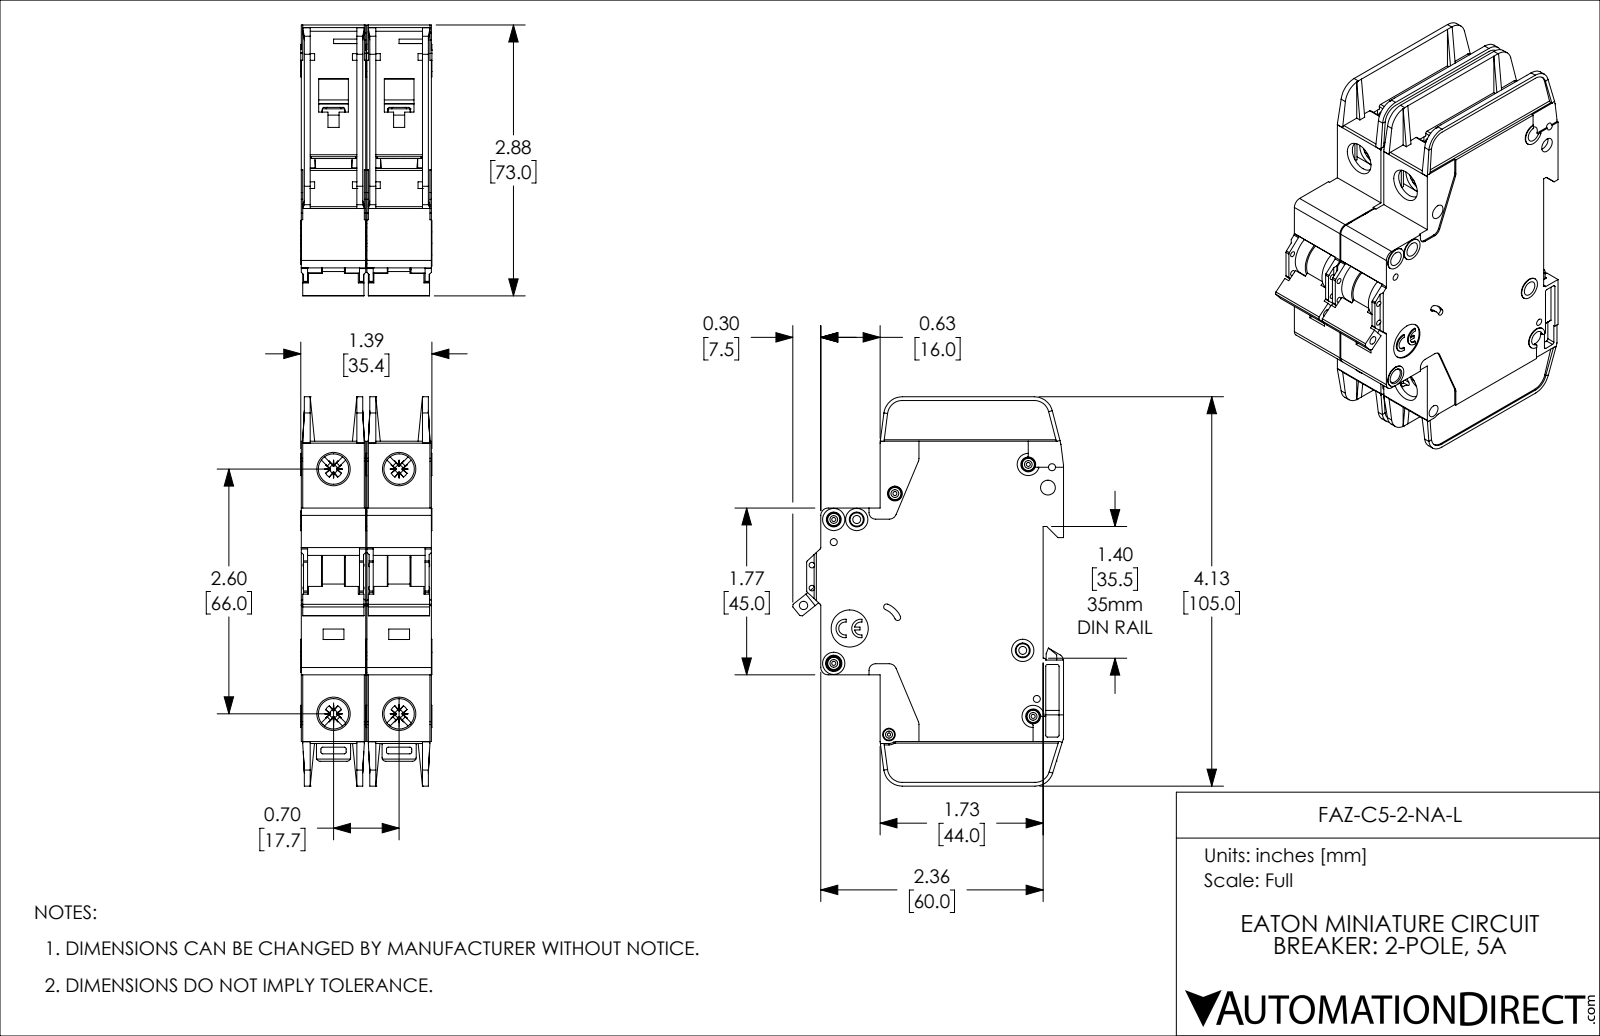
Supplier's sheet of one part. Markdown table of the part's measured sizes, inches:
| quantity | value |
| --- | --- |
| part name | FAZ-C5-2-NA-L |
| STEP written by | SolidWorks 2019 (AUTOMOTIVE_DESIGN) |
| units | inches |
| bodies | 2 solids, 2254 faces (1342 planar, 714 cylindrical, 198 other) |
| overall size | 4.134 × 2.876 × 1.394 |
| volume | 9.365 in³ |
| surface area | 82.01 in² |
| round holes (diameter × count) | 0.157 × 8, 0.043 × 5, 0.075 × 4, 0.323 × 4, 0.059 × 2, 0.085 × 2, 0.035 × 1, 0.089 × 1, 0.098 × 1, 0.134 × 1, 0.394 × 1 |
| round bosses / shafts (diameter × count) | 0.13 × 5, 0.236 × 4, 0.118 × 3, 0.098 × 2 |
| partial cylindrical surfaces (radius × count) | 0.02 × 57, 0.016 × 20, 0.039 × 14, 0.079 × 10, 0.043 × 8, 0.008 × 5, 0.197 × 5, 0.01 × 4 |
| main face-to-face distances | 0.697, 0.047, 0.685, 0.591, 0.094, 0.638, 0.543, 1.382, 0.744, 0.65 |
| hole center spacings | 0.244, 0.537, 0.697, 0.87, 2.598, 2.69, 0.189, 0.199 |
